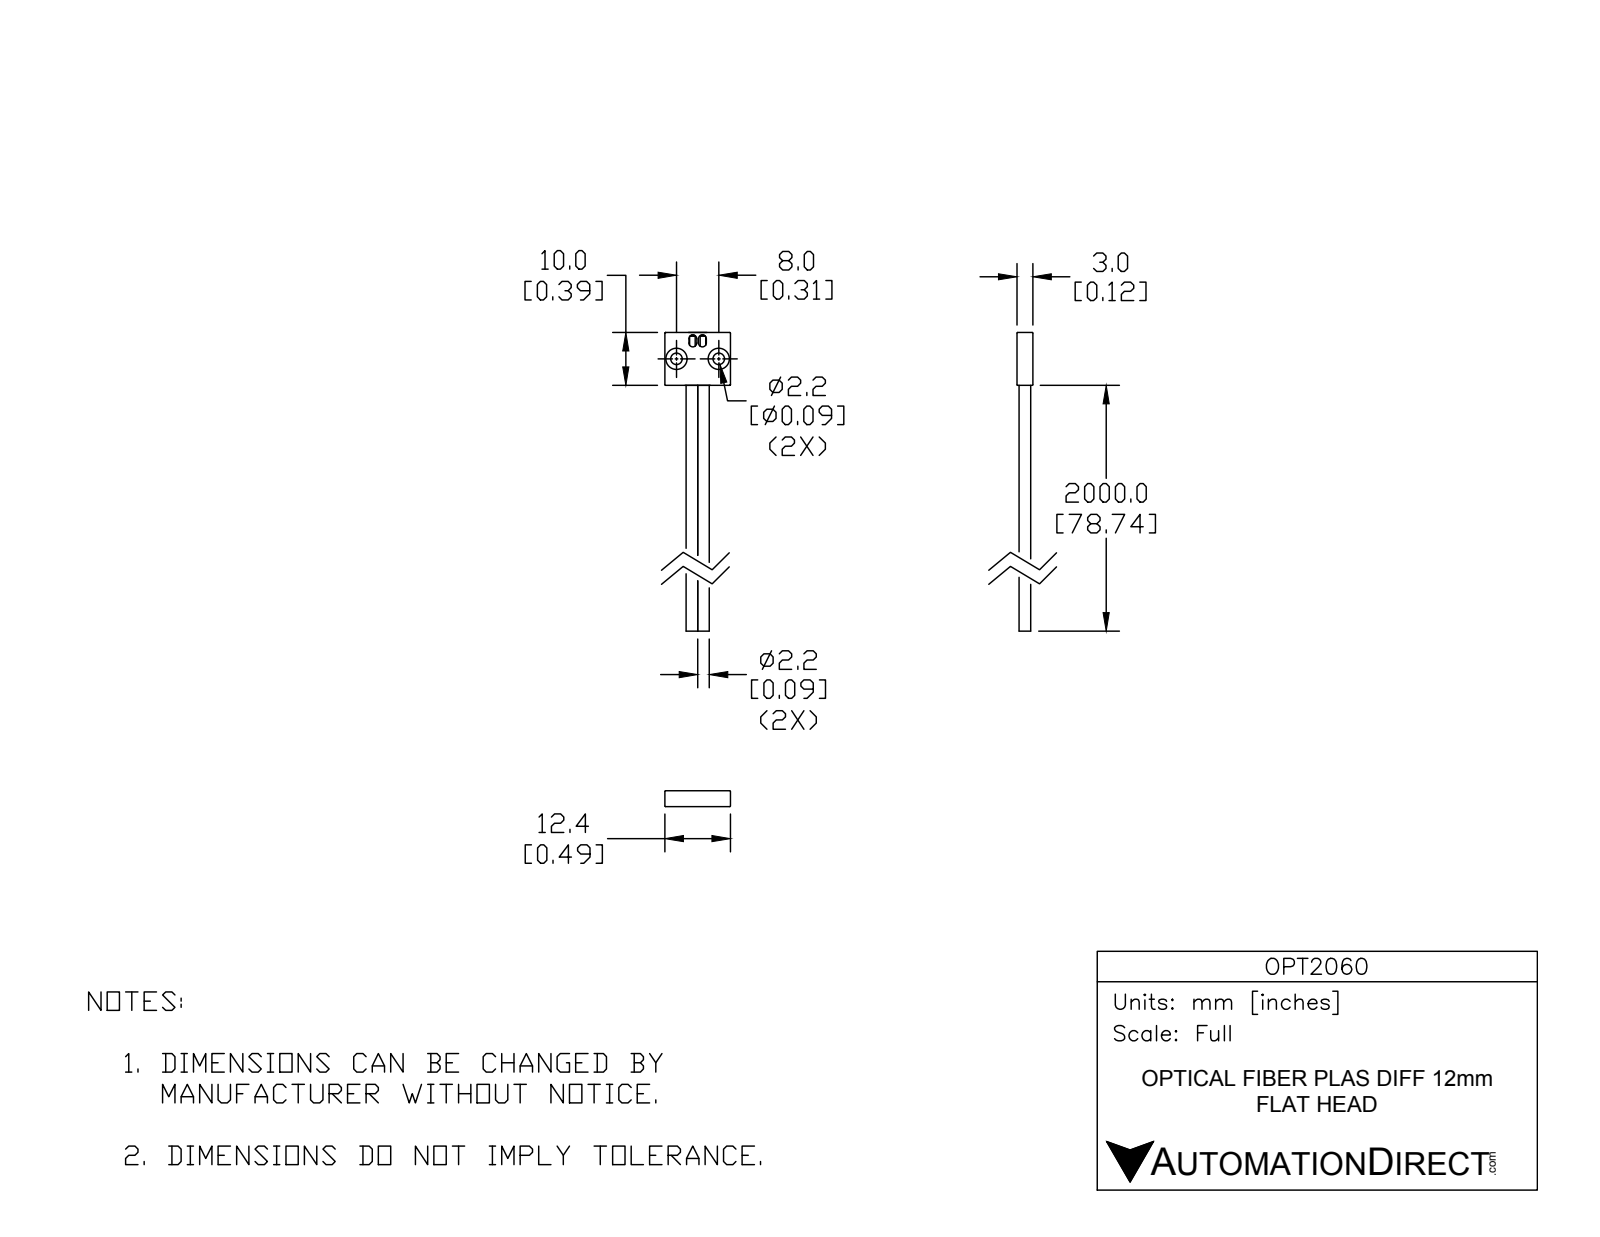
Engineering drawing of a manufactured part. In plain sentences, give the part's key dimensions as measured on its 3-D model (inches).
The part is named "OPT2060". Its 3-D file was written by "SolidWorks 2014 (AUTOMOTIVE_DESIGN)". It is 1 solid with 76 faces: 45 planar, 28 cylindrical and 3 other. Overall it measures 2.224 by 0.488 by 0.118 inches. Its volume is 0.04 cubic inches and its surface area 1.687 square inches. Round holes: 2 of diameter 0.087, 2 of diameter 0.157. Round bosses or shafts: 2 of diameter 0.087. Partial cylindrical surfaces (rounded edges, fillets, slot ends): 4 of radius 0.03, 2 of radius 0.024. The main face-to-face distances are 0.118, 0.488, 0.394, 0.067, 0.051, 1.831, 2.224, 0.043, 0.075, 0.071. The hole center spacings are 0.315.
